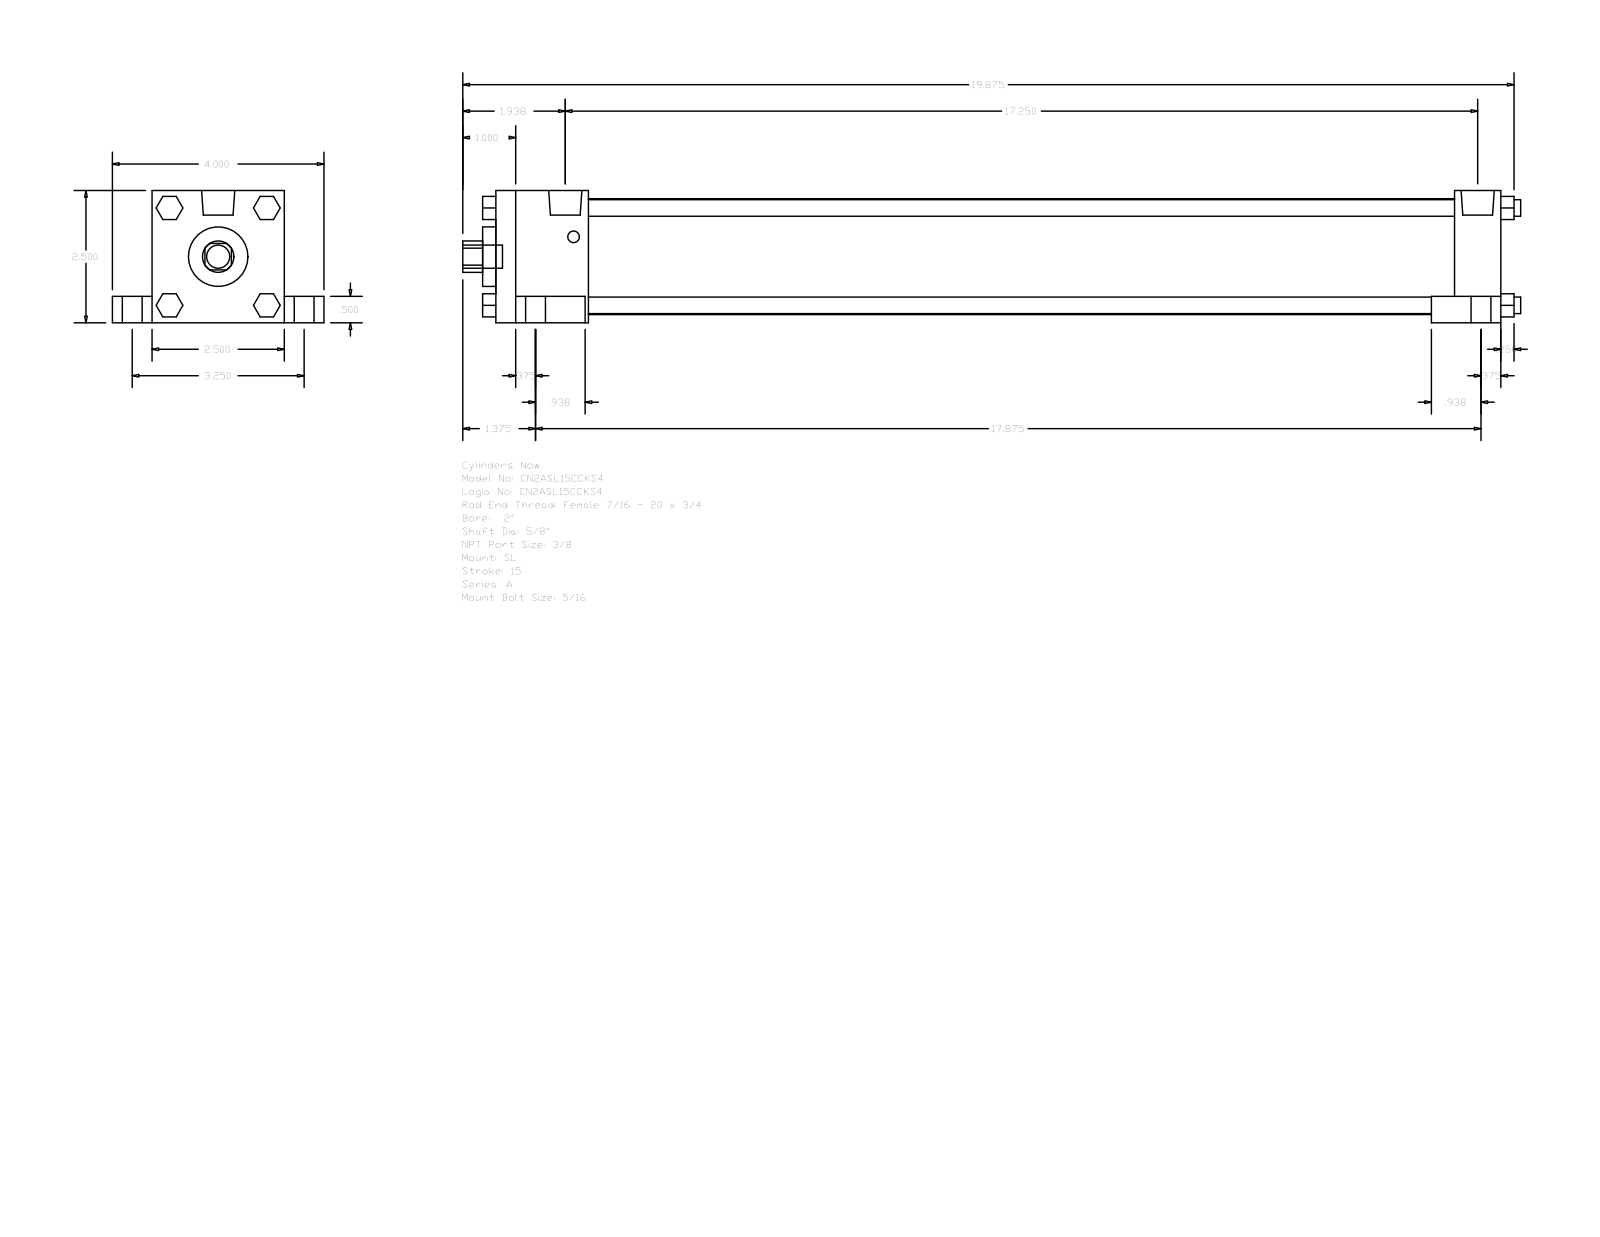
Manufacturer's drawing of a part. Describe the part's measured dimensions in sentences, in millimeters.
The part is named "A_SL__0200_0.625". Its 3-D file was written by "GSSL Pune (CONFIG_CONTROL_DESIGN)". It is 0 solids with 148 faces: 112 planar, 36 cylindrical and 0 other. Overall it measures 508 by 101.6 by 63.5 millimeters. Round holes: 1 of diameter 15.88, 1 of diameter 28.57, 1 of diameter 55.63. Round bosses or shafts: 4 of diameter 15.88, 4 of diameter 9.53, 4 of diameter 7.94, 4 of diameter 5.56, 2 of diameter 15.93, 1 of diameter 11.11. Partial cylindrical surfaces (rounded edges, fillets, slot ends): 1 of radius 7.54. The main face-to-face distances are 63.5, 482.6, 50.8, 12.7, 19.05, 82.55, 44.45, 438.15, 460.37, 415.92.
